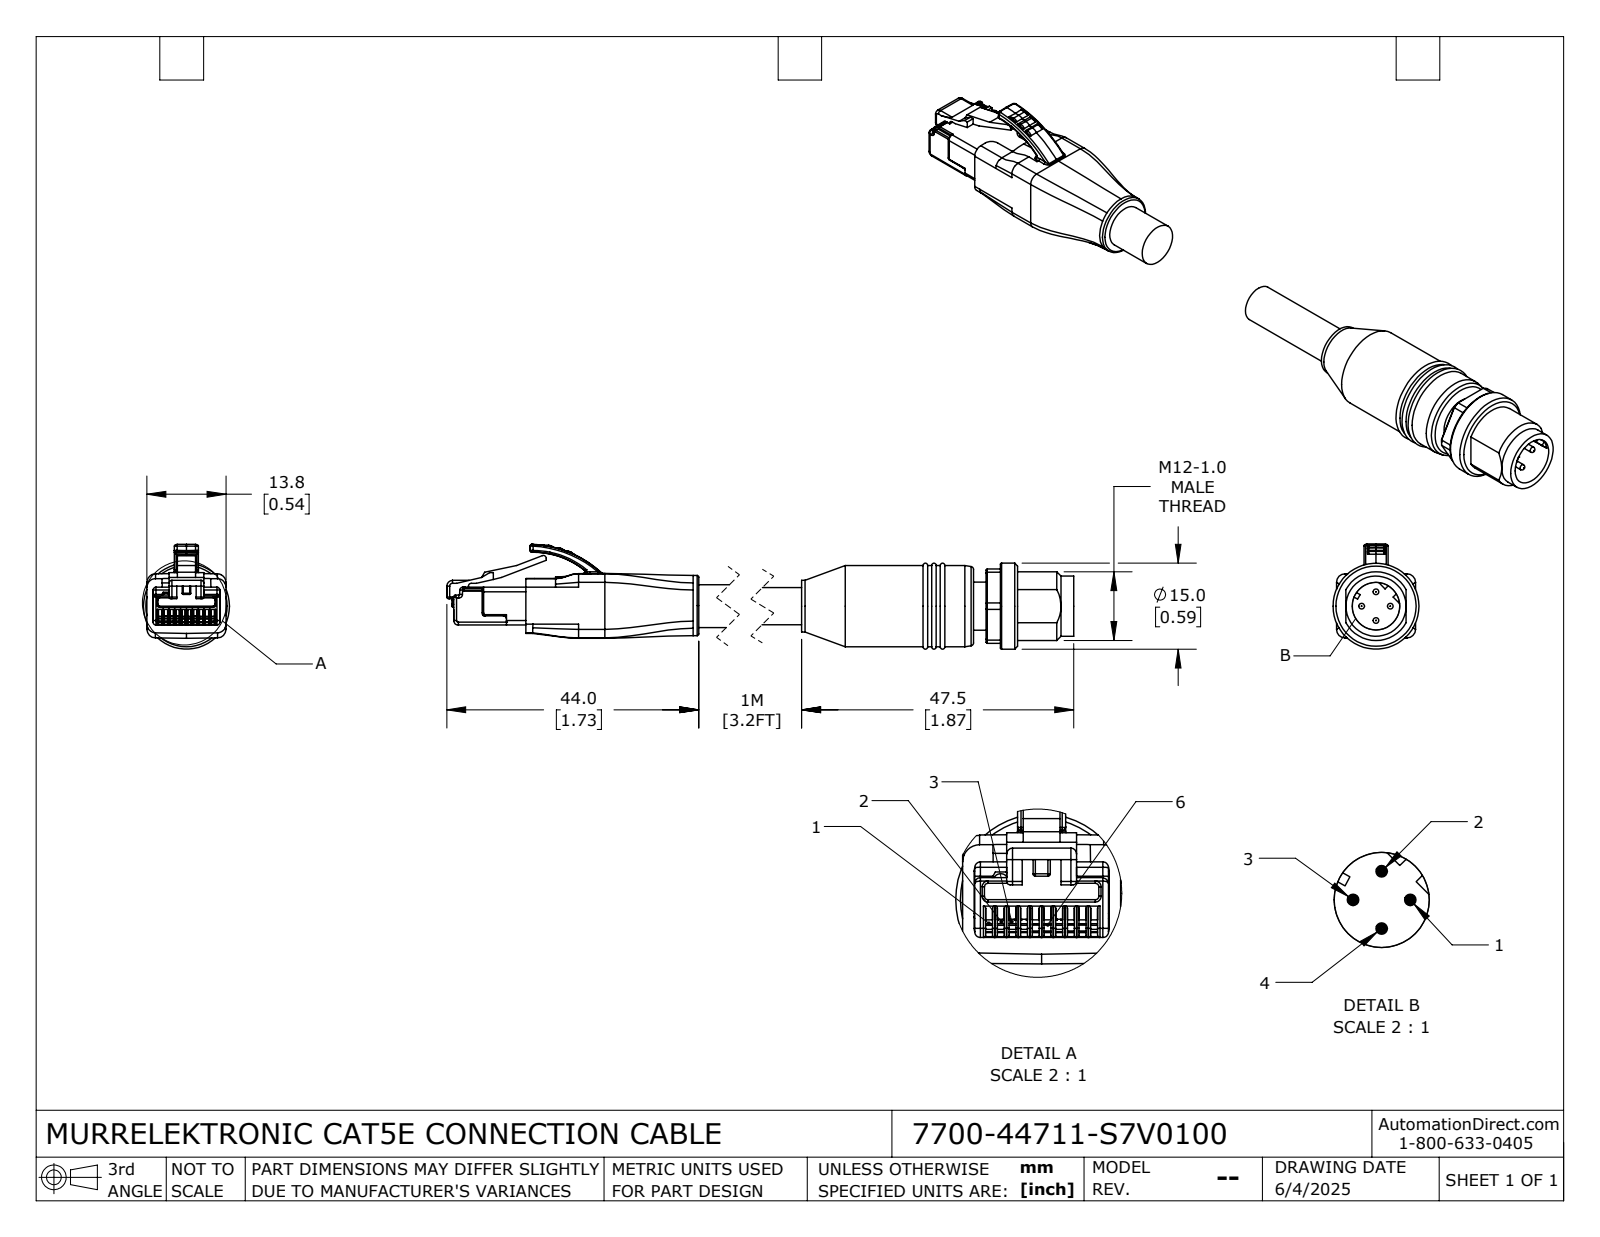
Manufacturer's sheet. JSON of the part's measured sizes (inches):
{"part_name": "7700-44711-S7V0100_MALE; 7700-44711-S7V0100; 7700-44711-S7V0100_RJ45", "step_written_by": "SolidWorks 2024 (CONFIG_CONTROL_DESIGN)", "units": "inches", "bodies": {"solids": 2, "faces": 757, "planar": 357, "cylindrical": 235, "other": 165}, "overall_size": [5.689, 0.72, 0.591], "volume_in3": 0.725, "surface_area_in2": 8.951, "round_holes": [[0.327, 1]], "round_bosses_or_shafts": [[0.039, 4], [0.413, 2], [0.591, 1], [0.559, 1], [0.354, 1], [0.331, 1], [0.295, 1], [0.256, 1]], "partial_cylinders_radius": [[0.008, 61], [0.02, 25], [0.012, 14], [0.059, 9], [0.031, 5], [0.021, 2], [0.197, 2], [0.005, 1]], "face_to_face_distances": [0.543, 0.087, 0.065, 0.478, 0.04, 0.504, 0.025, 0.439, 0.386, 0.035]}
